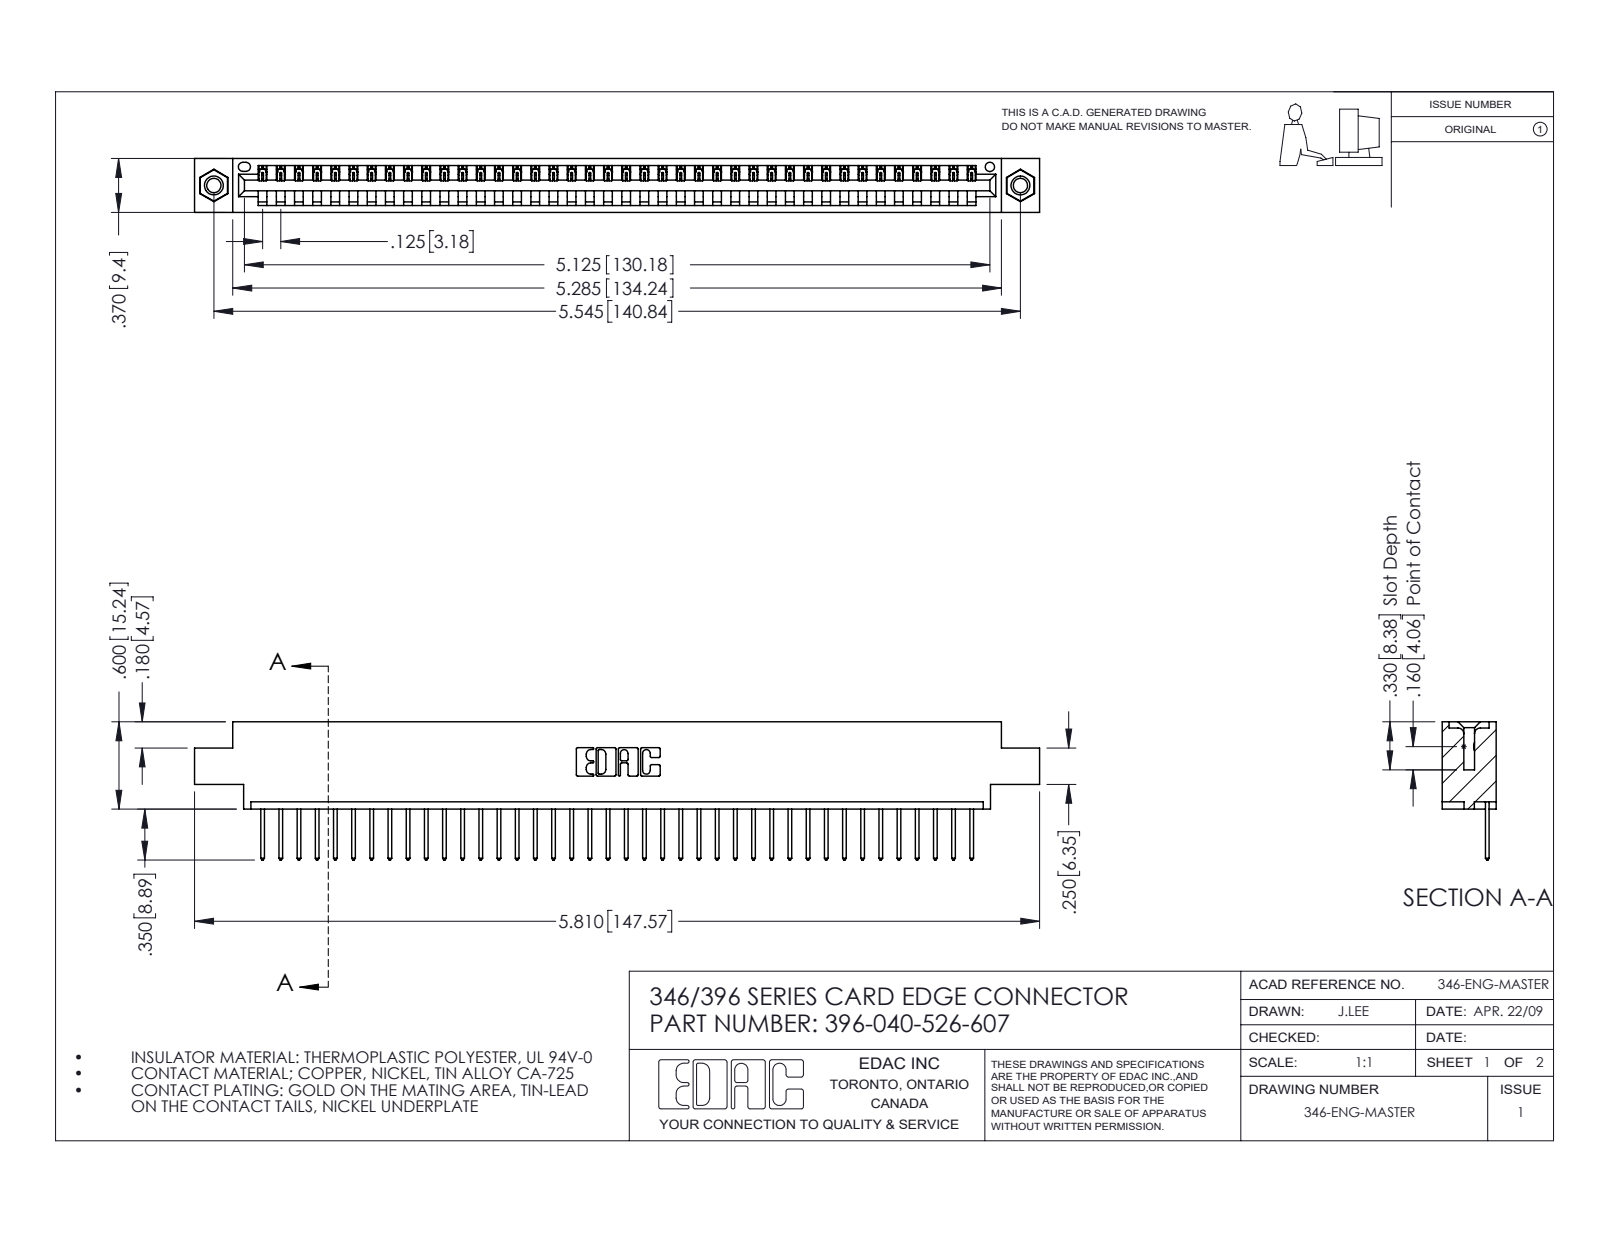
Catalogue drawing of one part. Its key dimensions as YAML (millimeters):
part_name: "345-250-001_345-250-005-103; 396-040-526-607; 345-292-001_345-293-126; 346 Part_0.170 Offset - 0.156 Dia-TI"
step_written_by: "SolidWorks 2016 (CONFIG_CONTROL_DESIGN)"
units: millimeters
bodies: {solids: 43, faces: 2506, planar: 1712, cylindrical: 778, other: 16}
overall_size: [147.6, 24.1, 9.4]
volume: 13900
surface_area: 17520
round_holes:
  - {diameter: 2.5, count: 2}
  - {diameter: 3.2, count: 2}
  - {diameter: 4, count: 2}
  - {diameter: 1.6, count: 1}
round_bosses_or_shafts:
  - {diameter: 3.9, count: 2}
partial_cylinders:
  - {radius: 0.2, count: 80}
  - {radius: 0.3, count: 80}
  - {radius: 0.3, count: 22}
  - {radius: 0.2, count: 6}
  - {radius: 0.8, count: 6}
  - {radius: 0.7, count: 3}
  - {radius: 0.8, count: 2}
  - {radius: 1, count: 2}
face_to_face_distances: [1.2, 8.2, 9.4, 6.4, 1.8, 7.6, 0.6, 5.6, 3.8, 2.5]
hole_center_spacings: [6.2, 135.5, 140.8]
